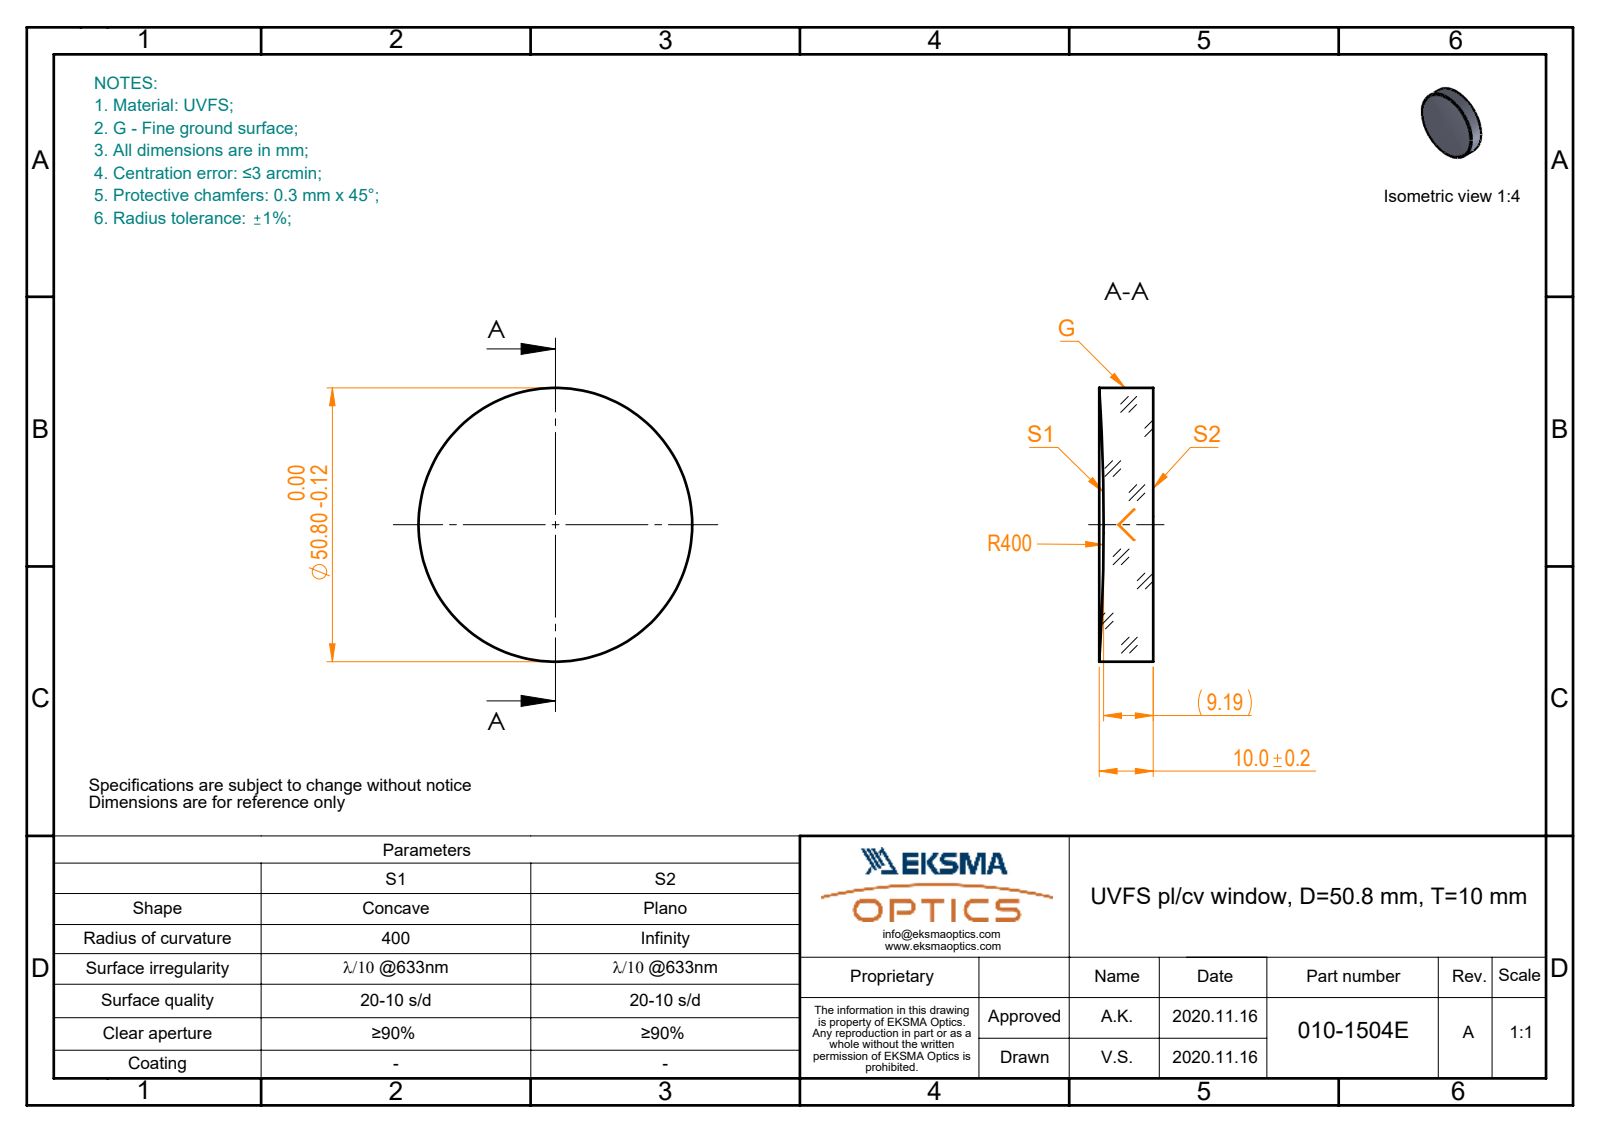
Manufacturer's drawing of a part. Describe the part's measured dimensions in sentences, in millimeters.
The part is named "010-1504E_UVFS_PCV_window". Its 3-D file was written by "SolidWorks 2019 (CONFIG_CONTROL_DESIGN)". It is 1 solid with 5 faces: 1 planar, 2 cylindrical and 2 other. Overall it measures 50.8 by 50.8 by 10 millimeters. Its volume is 19 450 cubic millimeters and its surface area 5 652 square millimeters. Round bosses or shafts: 1 of diameter 50.8.
